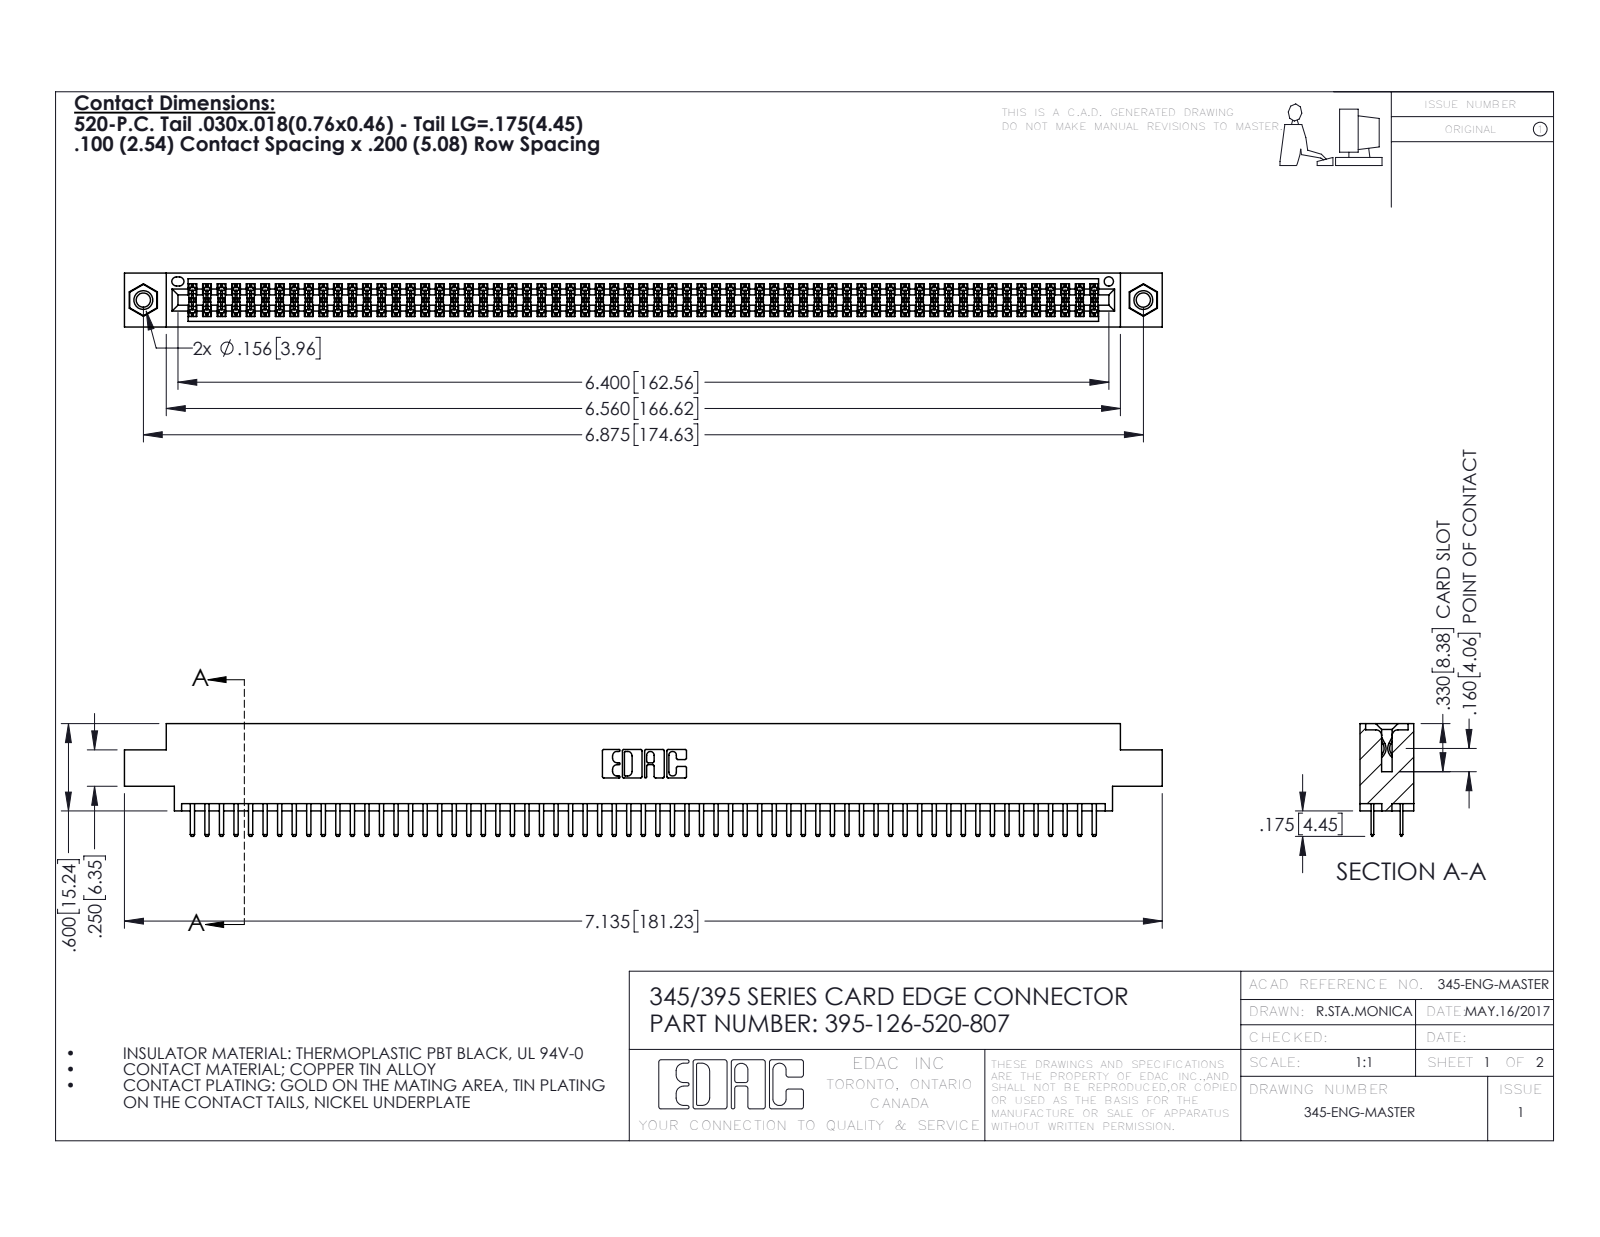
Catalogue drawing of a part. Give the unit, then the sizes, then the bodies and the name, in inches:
Units: inches
Overall size (bounding box): 7.135 × 0.775 × 0.37
Round holes (diameter × count): ⌀0.098 ×2, ⌀0.125 ×2, ⌀0.156 ×2, ⌀0.064 ×1
Round bosses / shafts (diameter × count): ⌀0.155 ×2
Partial cylindrical surfaces — rounded edges, fillets, slot ends (radius × count): R0.006 ×189, R0.01 ×130, R0.01 ×22, R0.007 ×6, R0.031 ×6, R0.026 ×3, R0.014 ×2, R0.019 ×2
Main face-to-face distances: 0.072, 0.298, 0.2, 0.37, 0.098, 0.272, 0.025, 0.225, 0.022, 0.072
Hole centre spacings: 0.27, 6.639, 6.875
Volume: 1.075 in³ · Surface area: 41.08 in²
Bodies: 129 solids, 6994 faces (4526 planar, 2452 cylindrical, 16 other)
Part name (STEP PRODUCT): 345-250-001_345-250-005-103; 345 Part_0.170 Offset - 0.156 Dia-TI; 345-292-001_345-293-120; 395-126-520-807
STEP written by: SolidWorks 2016 (CONFIG_CONTROL_DESIGN)
